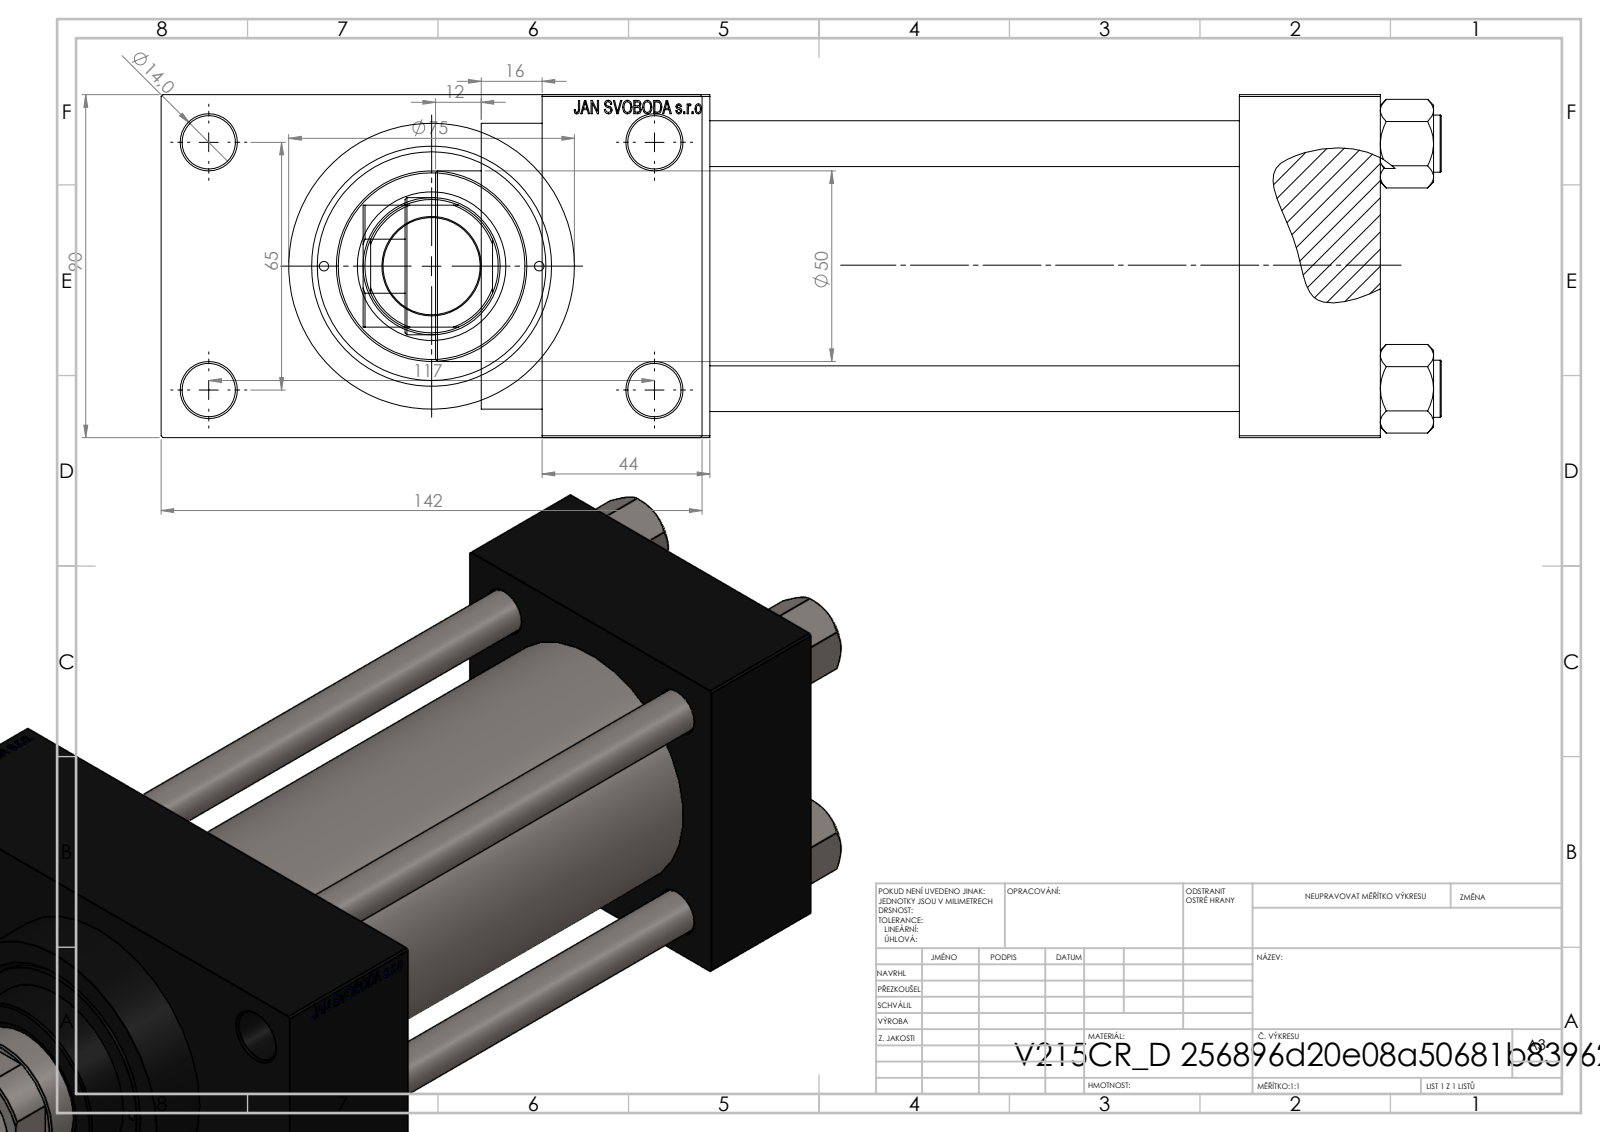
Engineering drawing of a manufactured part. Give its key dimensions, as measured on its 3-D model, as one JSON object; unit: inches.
{"part_name": "V215_VC_A; NUT_M5_D; V215CR_VCP_D; V215CR_D_Body (+1 more)", "step_written_by": "SolidWorks 2019 (CONFIG_CONTROL_DESIGN)", "units": "inches", "bodies": {"solids": 11, "faces": 1111, "planar": 499, "cylindrical": 92, "other": 520}, "overall_size": [11.142, 5.591, 3.543], "volume_in3": 78.05, "surface_area_in2": 403, "round_holes": [[0.472, 4], [0.551, 4], [0.098, 2], [0.276, 2], [0.825, 2], [1.181, 2], [1.004, 1], [1.417, 1], [1.535, 1], [1.969, 1], [2.362, 1], [2.48, 1]], "round_bosses_or_shafts": [[0.591, 4], [2.953, 1], [2.717, 1]], "partial_cylinders_radius": [[0.689, 1]], "face_to_face_distances": [3.543, 5.472, 1.457, 6.929, 8.661, 7.205, 1.732, 1.024, 4.567, 5.591], "hole_center_spacings": [1.037, 1.275, 1.748, 1.79, 2.531, 2.635, 2.694, 2.748]}
